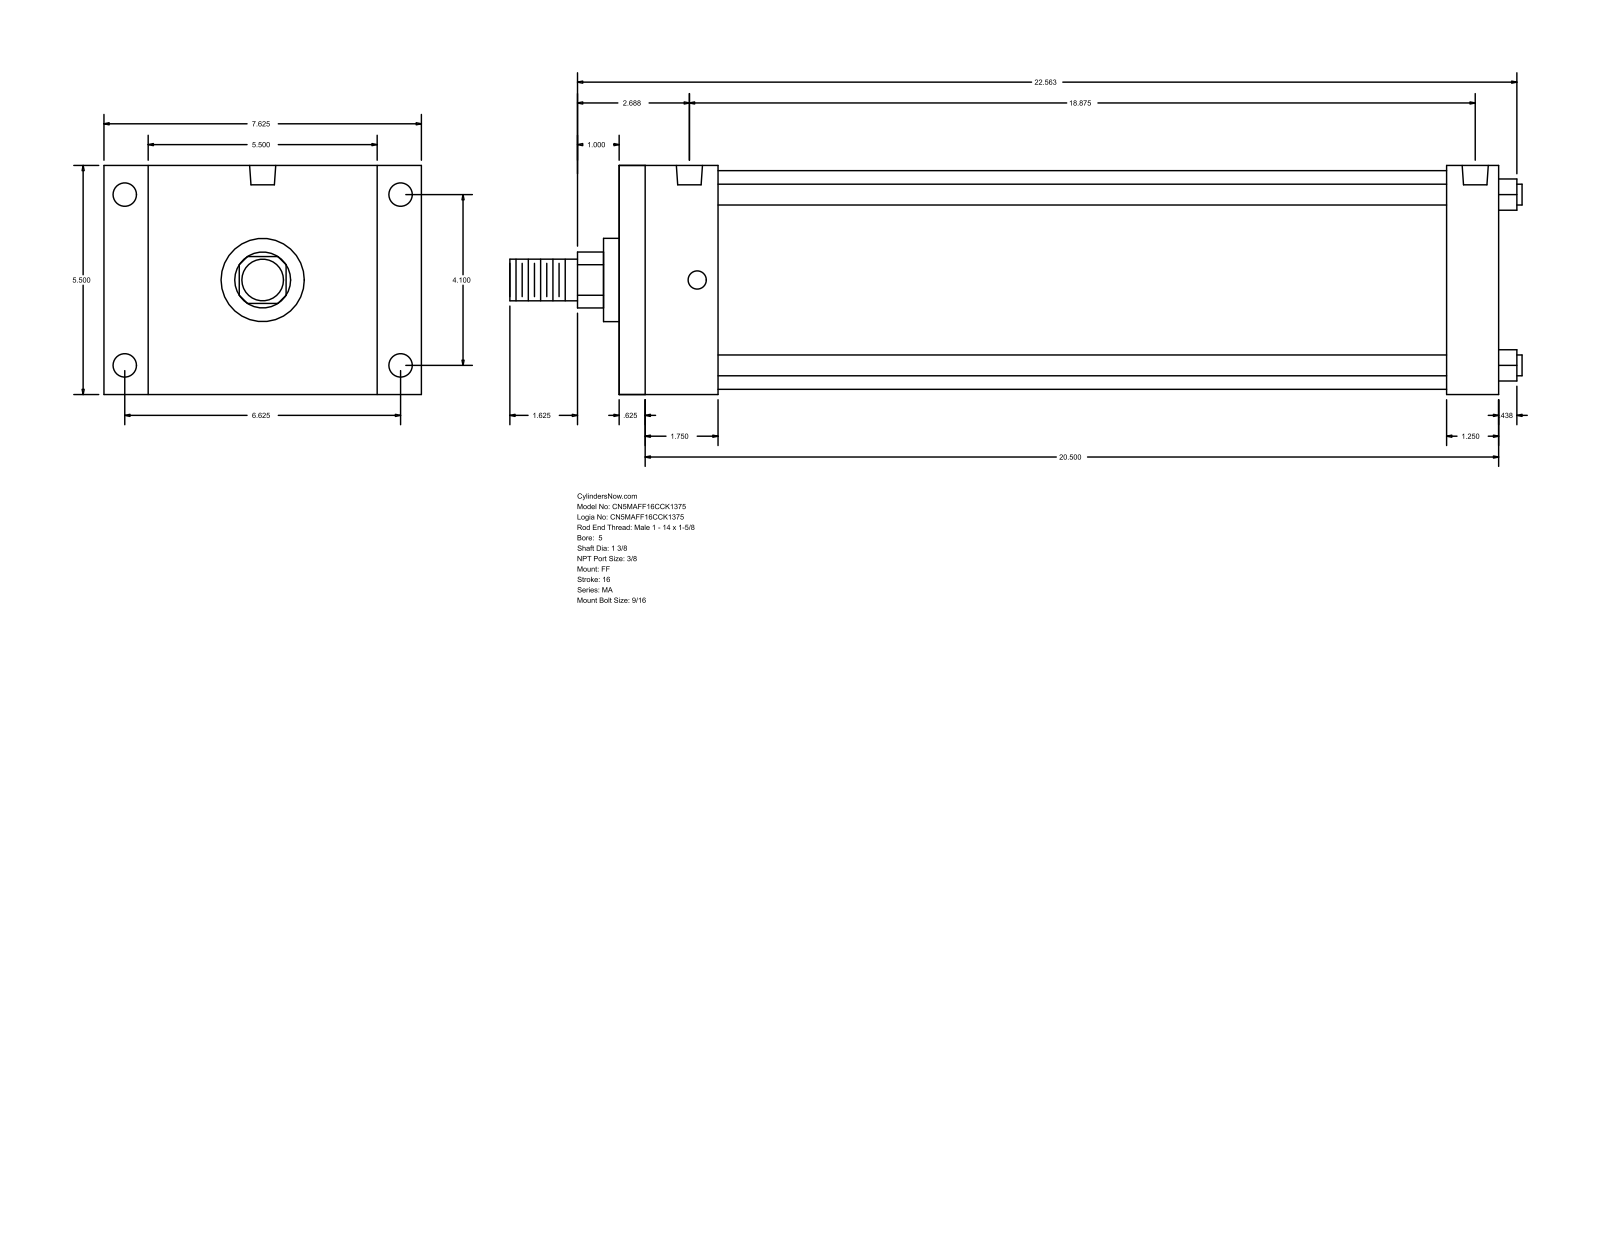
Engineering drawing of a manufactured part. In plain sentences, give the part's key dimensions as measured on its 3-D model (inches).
The part is named "MA_FF__0500_1.375". Its 3-D file was written by "GSSL Pune (CONFIG_CONTROL_DESIGN)". It is 0 solids with 92 faces: 64 planar, 28 cylindrical and 0 other. Overall it measures 24.313 by 7.625 by 5.5 inches. Round holes: 4 of diameter 0.437, 4 of diameter 0.563, 2 of diameter 0.627. Round bosses or shafts: 4 of diameter 0.5, 1 of diameter 5.25, 1 of diameter 2, 1 of diameter 1.375, 1 of diameter 1. Partial cylindrical surfaces (rounded edges, fillets, slot ends): 1 of radius 0.672. The main face-to-face distances are 5.5, 21.125, 0.625, 20.5, 19.875, 19.25, 1.25, 2.375, 1.75, 17.5. The hole center spacings are 0.188, 4.1, 6.625, 7.791, 18.5, 18.687, 18.875.
